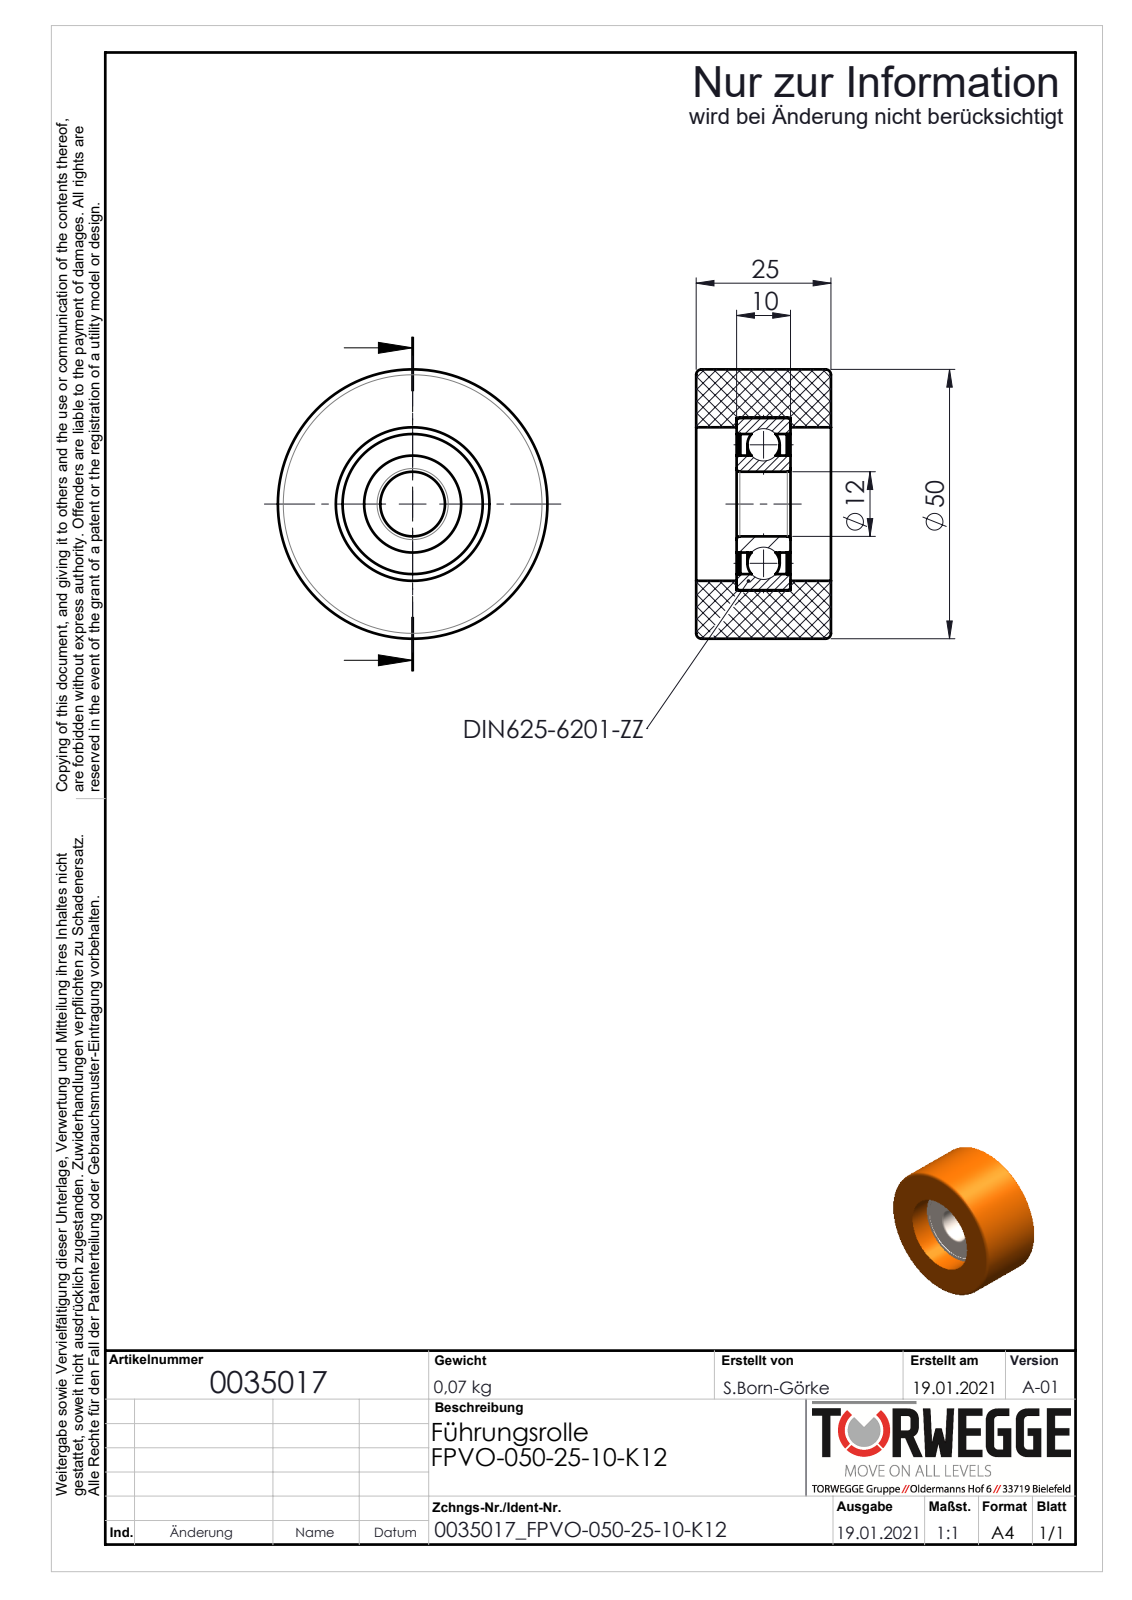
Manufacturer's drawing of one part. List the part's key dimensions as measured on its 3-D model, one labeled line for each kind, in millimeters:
Part name (STEP PRODUCT): 0035017
STEP written by: SolidWorks 2018 (AUTOMOTIVE_DESIGN)
Units: millimetres
Bodies: 4 solids, 56 faces (12 planar, 28 cylindrical, 16 other)
Overall size (bounding box): 50 × 50 × 25
Volume: 37 337 mm³ · Surface area: 13 877 mm²
Round holes (diameter × count): ⌀12 ×1, ⌀18 ×1, ⌀26 ×1, ⌀28.5 ×1, ⌀32 ×1
Round bosses / shafts (diameter × count): ⌀50 ×1
Main face-to-face distances: 25, 7.5, 17.5, 7.7, 8.2, 16.8, 17.3, 0.7, 9.3, 9.8
